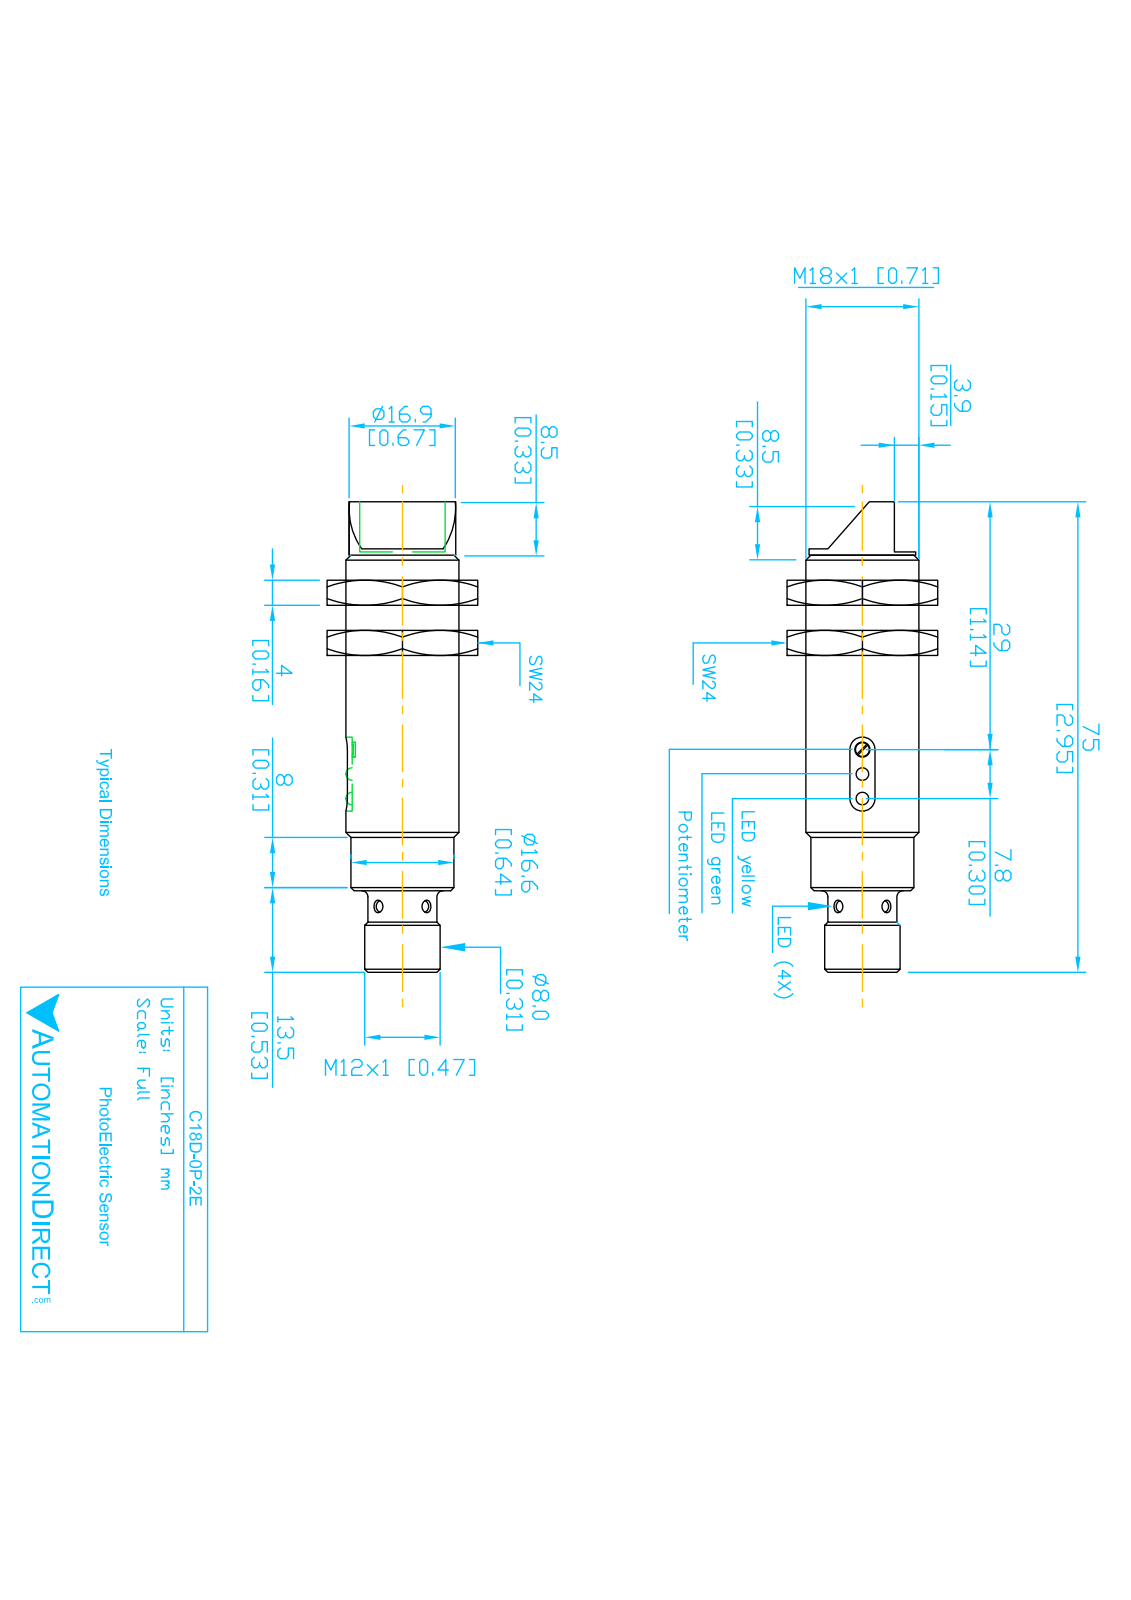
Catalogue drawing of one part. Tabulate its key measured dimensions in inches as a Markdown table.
| quantity | value |
| --- | --- |
| part name | C18D-0P-2E |
| STEP written by | SolidWorks 2017 (AUTOMOTIVE_DESIGN) |
| units | inches |
| bodies | 4 solids, 90 faces (21 planar, 36 cylindrical, 33 other) |
| overall size | 2.839 × 0.709 × 0.709 |
| volume | 0.885 in³ |
| surface area | 9.153 in² |
| round holes (diameter × count) | 0.118 × 2, 0.335 × 1 |
| round bosses / shafts (diameter × count) | 0.04 × 4, 0.709 × 1, 0.665 × 1, 0.646 × 1, 0.619 × 1, 0.459 × 1, 0.415 × 1 |
| partial cylindrical surfaces (radius × count) | 0.015 × 6, 0.02 × 3, 0.202 × 1 |
| main face-to-face distances | 1.988, 0.1, 1.888, 0.092, 1.98, 2.158, 2.15, 2.058, 0.17, 2.5 |
